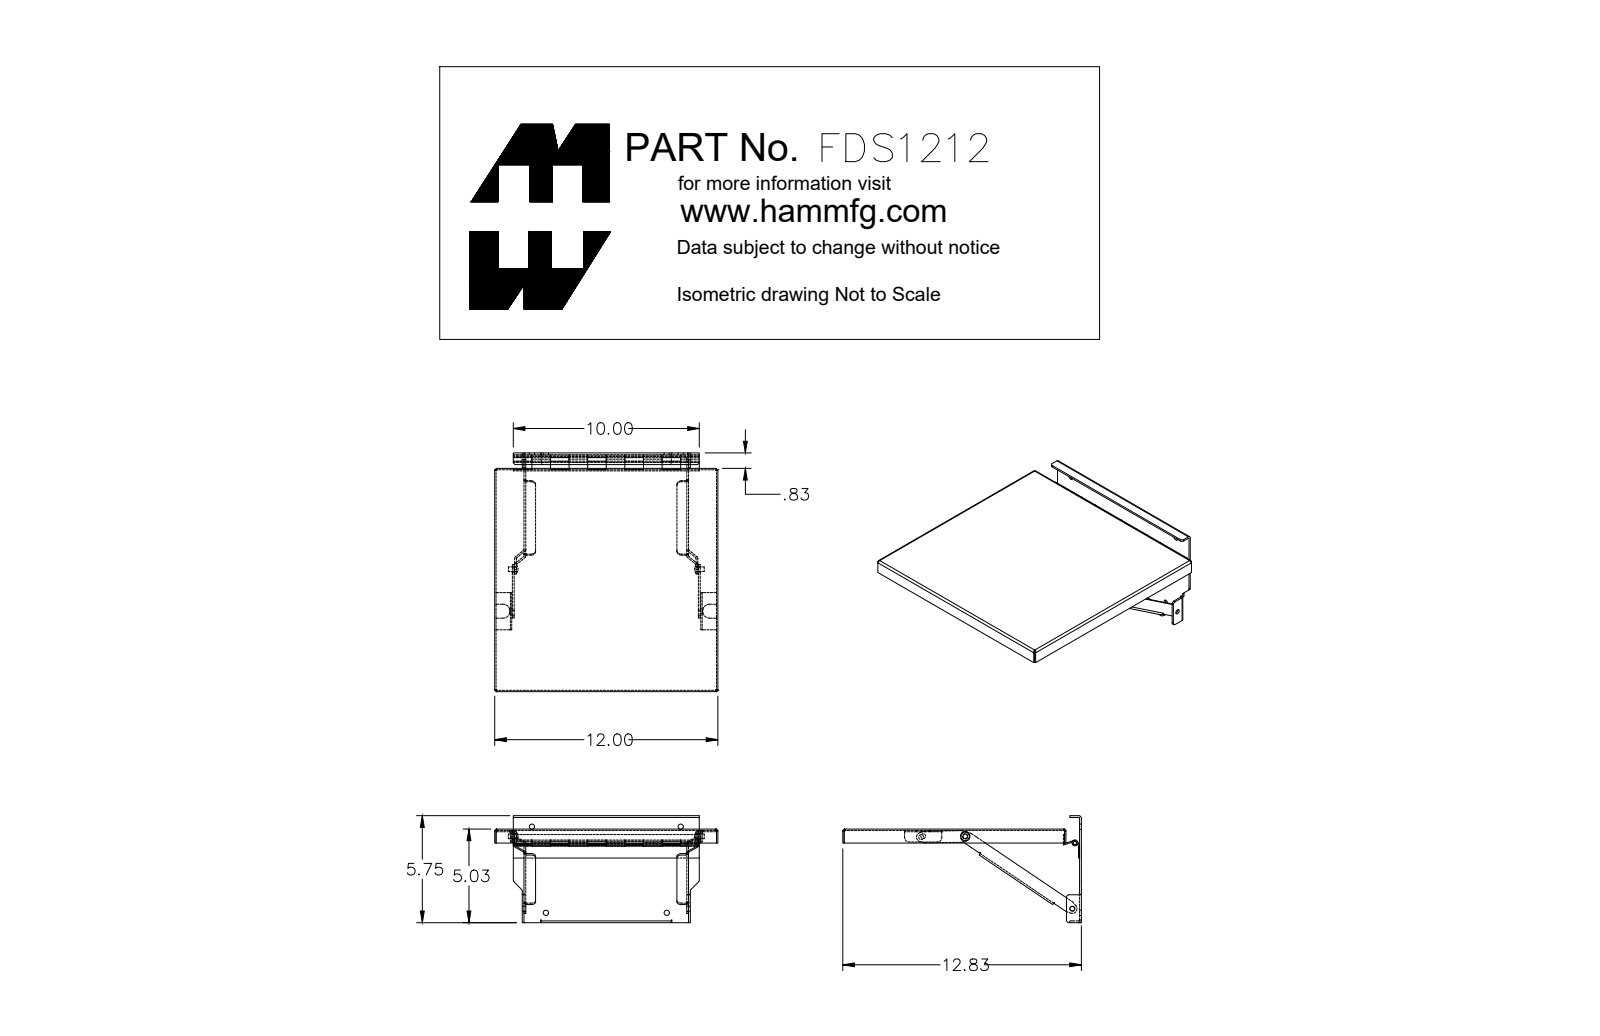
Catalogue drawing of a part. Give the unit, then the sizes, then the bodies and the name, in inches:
Units: inches
Overall size (bounding box): 12.831 × 12 × 5.75
Round holes (diameter × count): ⌀0.281 ×4, ⌀0.257 ×2, ⌀0.265 ×2, ⌀0.265 ×2, ⌀0.187 ×1, ⌀0.2 ×1, ⌀0.26 ×1
Round bosses / shafts (diameter × count): ⌀0.51 ×1, ⌀0.5 ×1, ⌀0.32 ×1, ⌀0.25 ×1
Partial cylindrical surfaces — rounded edges, fillets, slot ends (radius × count): R0.25 ×12, R0.048 ×10, R0.125 ×10, R0.143 ×10, R0.036 ×6, R0.108 ×6, R0.375 ×2
Main face-to-face distances: 0.072, 0.095, 11.928, 0.095, 11.856, 12, 0.625, 0.808, 0.903, 0.06
Hole centre spacings: 8.6, 0.111, 2.256, 2.367, 3.535, 4.685, 4.685, 5.913
Volume: 22.53 in³ · Surface area: 594.9 in²
Bodies: 15 solids, 386 faces (218 planar, 156 cylindrical, 12 other)
Part name (STEP PRODUCT): FDS1212GY
STEP written by: SolidWorks 2018 (AUTOMOTIVE_DESIGN)
